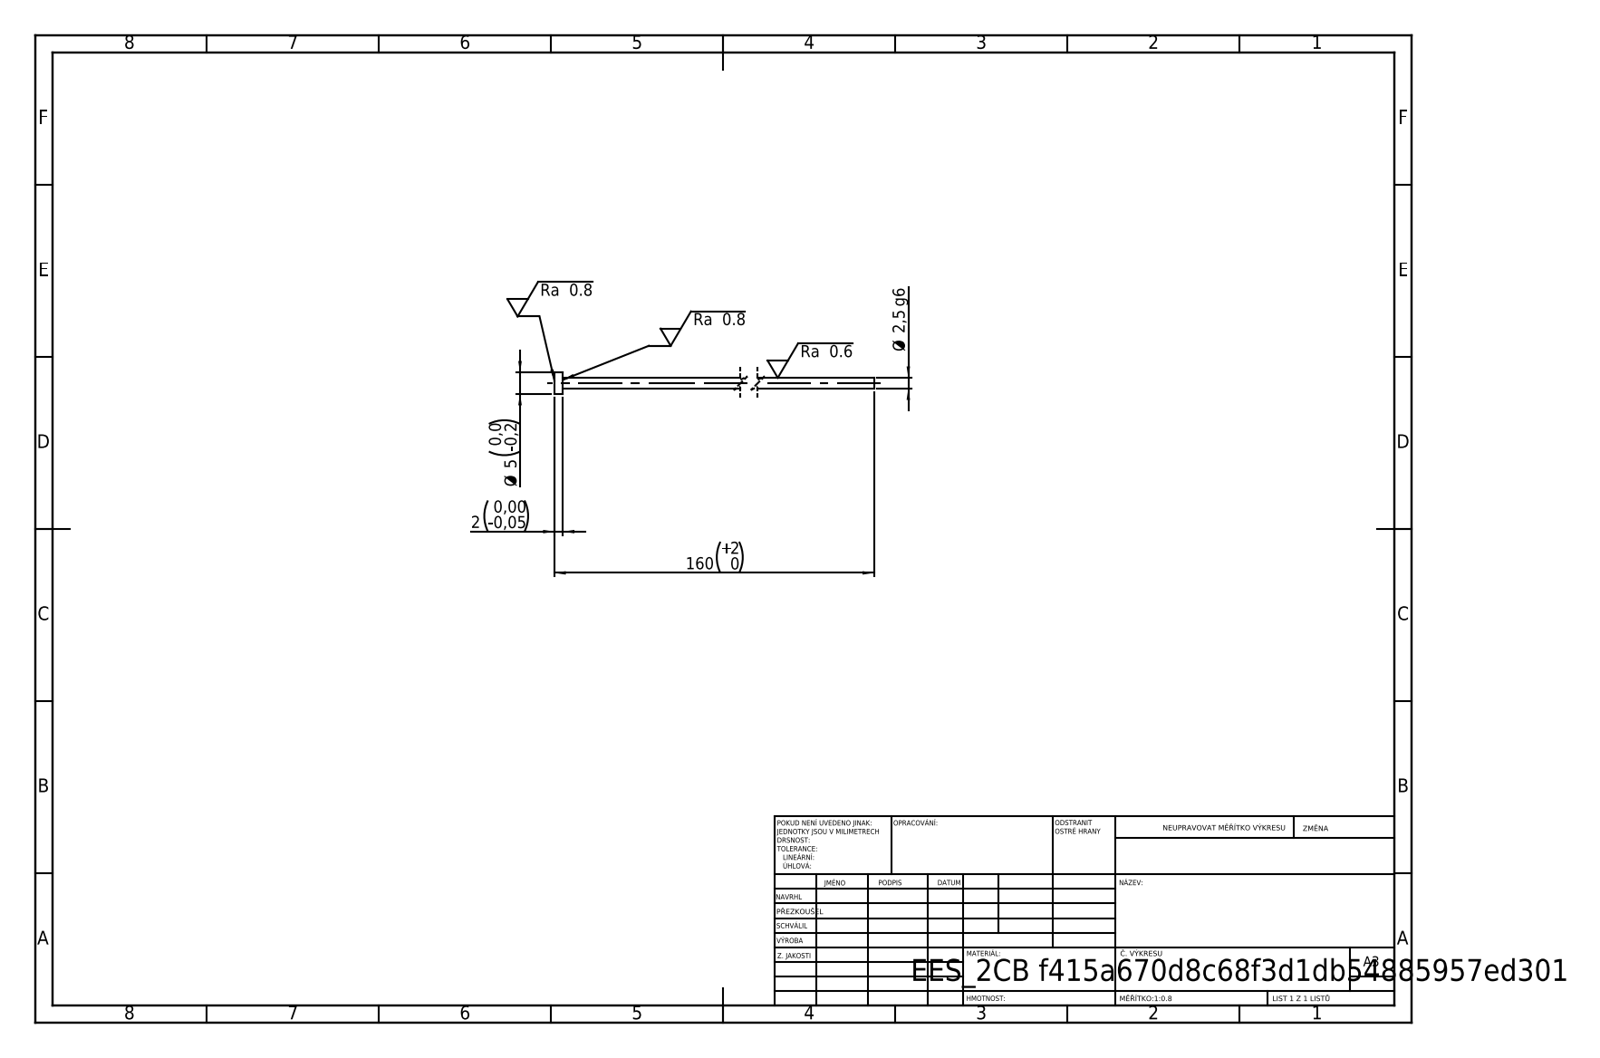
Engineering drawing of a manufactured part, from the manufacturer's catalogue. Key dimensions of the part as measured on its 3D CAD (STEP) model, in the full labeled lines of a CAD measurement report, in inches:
STEP written by: SolidWorks 2019 (CONFIG_CONTROL_DESIGN)
Units: inches
Bodies: 1 solid, 7 faces (3 planar, 4 cylindrical, 0 other)
Overall size (bounding box): 6.299 × 0.197 × 0.197
Volume: 0.05 in³ · Surface area: 2.034 in²
Round bosses / shafts (diameter × count): ⌀0.197 ×1, ⌀0.098 ×1
Main face-to-face distances: 0.079, 6.299, 6.22
